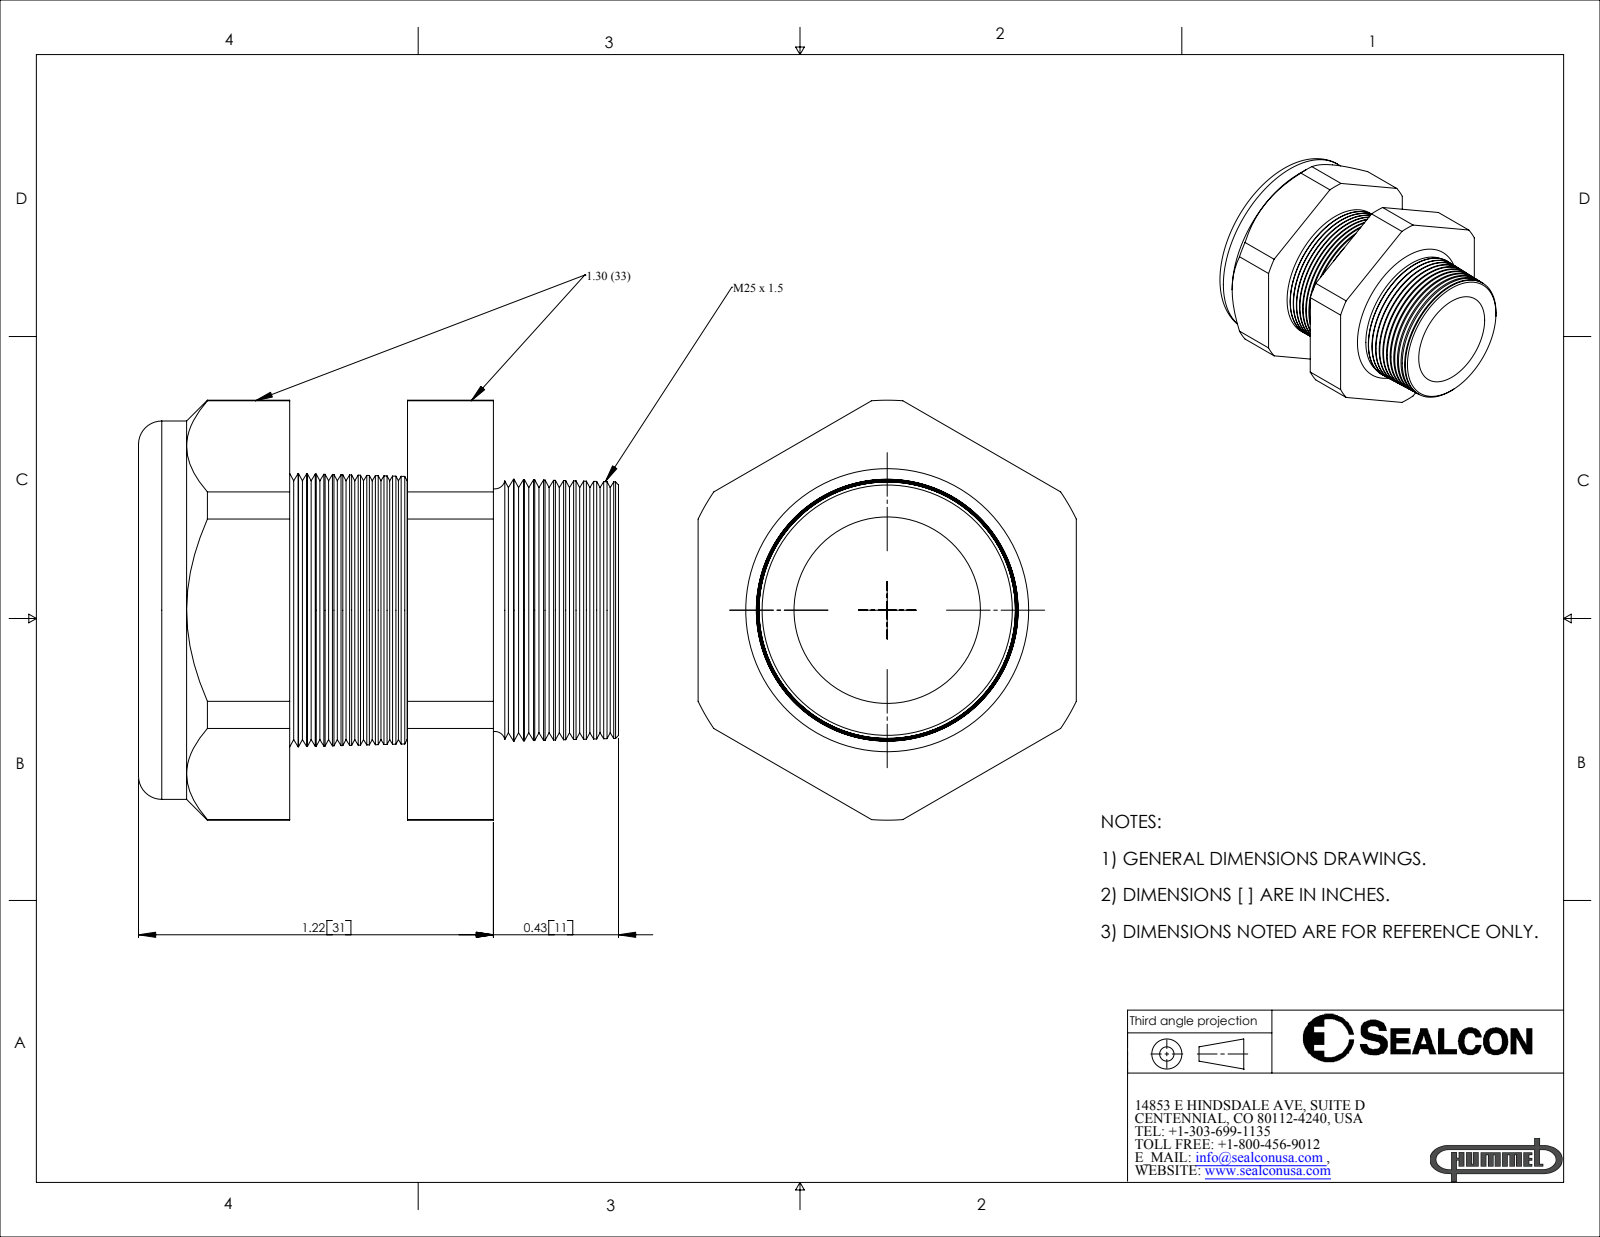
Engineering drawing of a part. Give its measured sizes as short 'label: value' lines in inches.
name: CD25MP-BK
written by: SolidWorks 2007 (CONFIG_CONTROL_DESIGN)
unit: in
bodies: 2 solids, 206 faces (20 planar, 20 cylindrical, 166 other)
size: 1.65 × 1.443 × 1.3
volume: 1.191 in³; area: 16.55 in²
holes: 1× ⌀0.69, 1× ⌀0.71
bosses: 1× ⌀1.3
rounds: 1× R0.721
face distances: 1.3, 0.405, 0.7, 0.295, 0.52, 0.925, 1.22, 0.35, 0.17, 0.575
